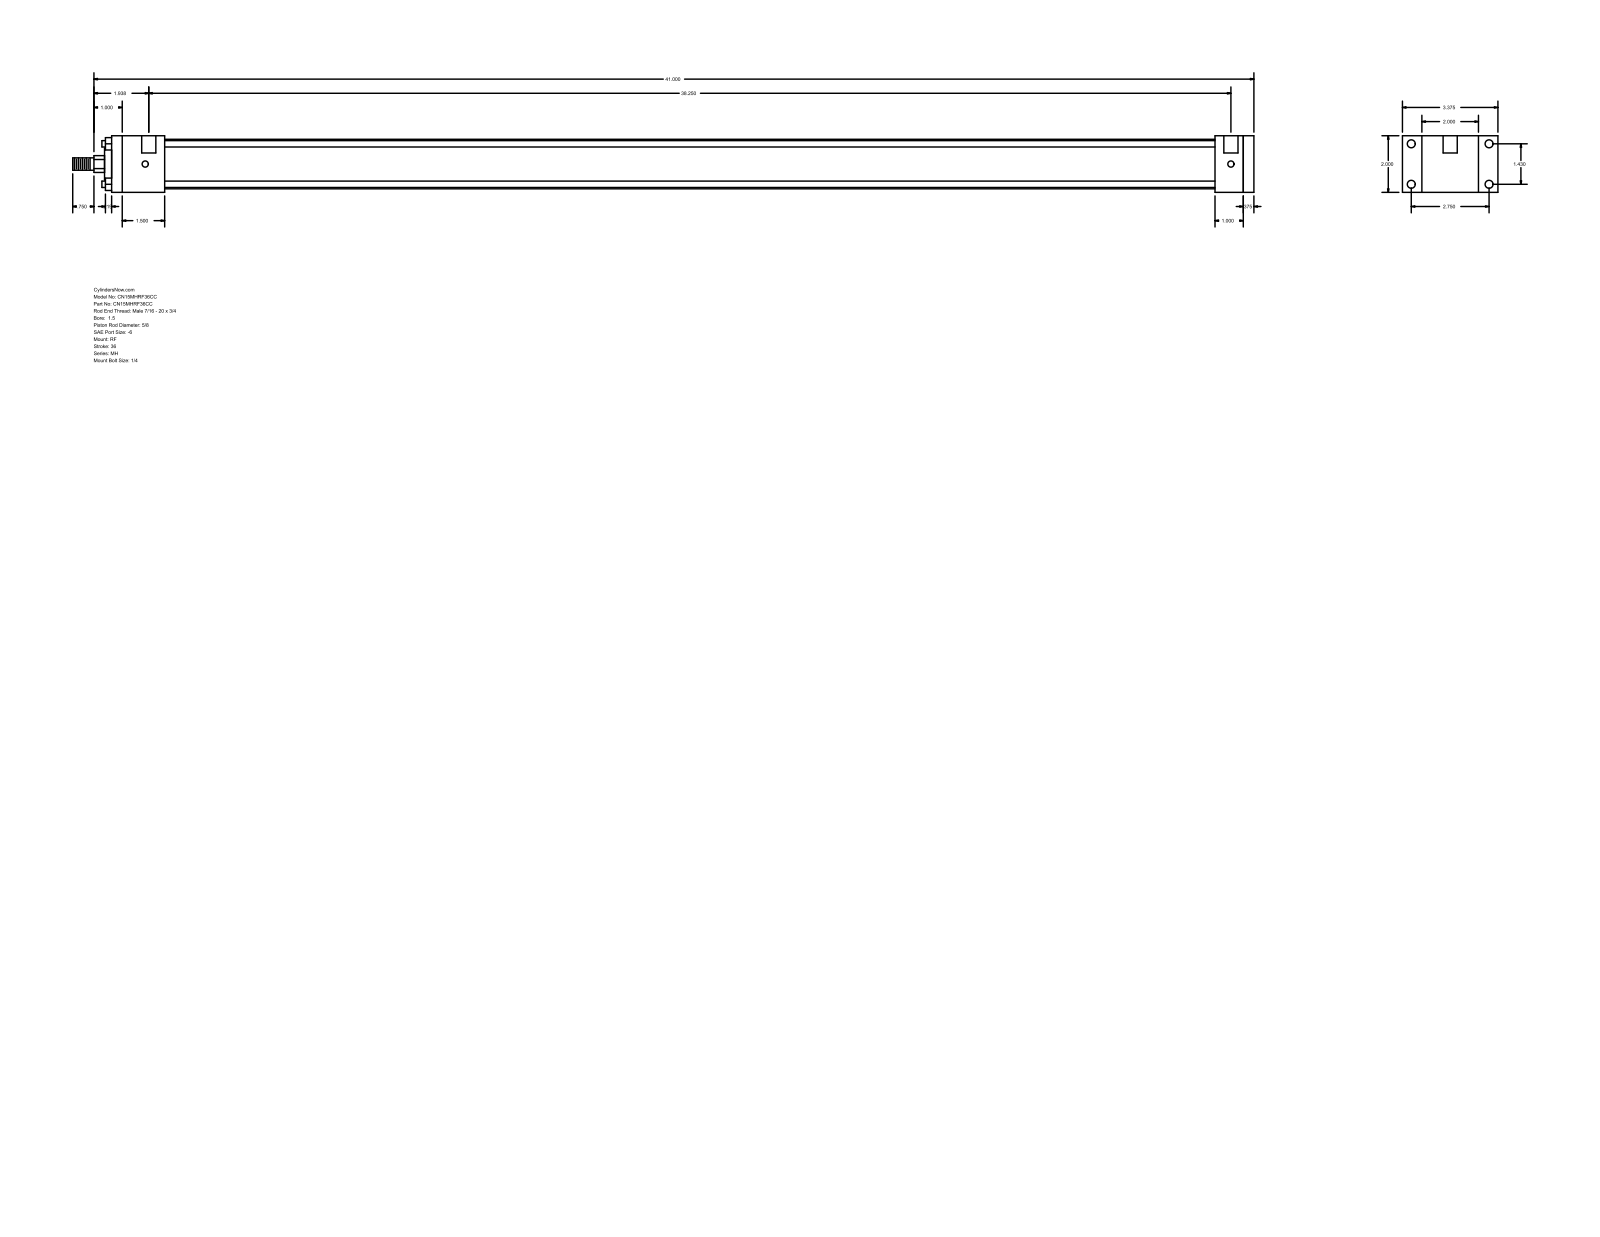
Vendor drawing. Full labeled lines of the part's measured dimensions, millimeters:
Part name (STEP PRODUCT): MH_RF__0150_0.625
STEP written by: GSSL Pune (CONFIG_CONTROL_DESIGN)
Units: millimetres
Bodies: 0 solids, 92 faces (64 planar, 28 cylindrical, 0 other)
Overall size (bounding box): 1060.45 × 85.72 × 50.8
Round holes (diameter × count): ⌀5.56 ×4, ⌀7.14 ×4, ⌀12.7 ×2
Round bosses / shafts (diameter × count): ⌀5.71 ×4, ⌀44.45 ×1, ⌀28.57 ×1, ⌀15.88 ×1, ⌀11.11 ×1
Partial cylindrical surfaces — rounded edges, fillets, slot ends (radius × count): R7.54 ×1
Main face-to-face distances: 50.8, 9.52, 1016, 1025.52, 25.4, 17.46, 68.26, 990.6, 34.92, 47.62
Hole centre spacings: 36.32, 69.84, 78.72, 974.72, 3.17, 971.55
